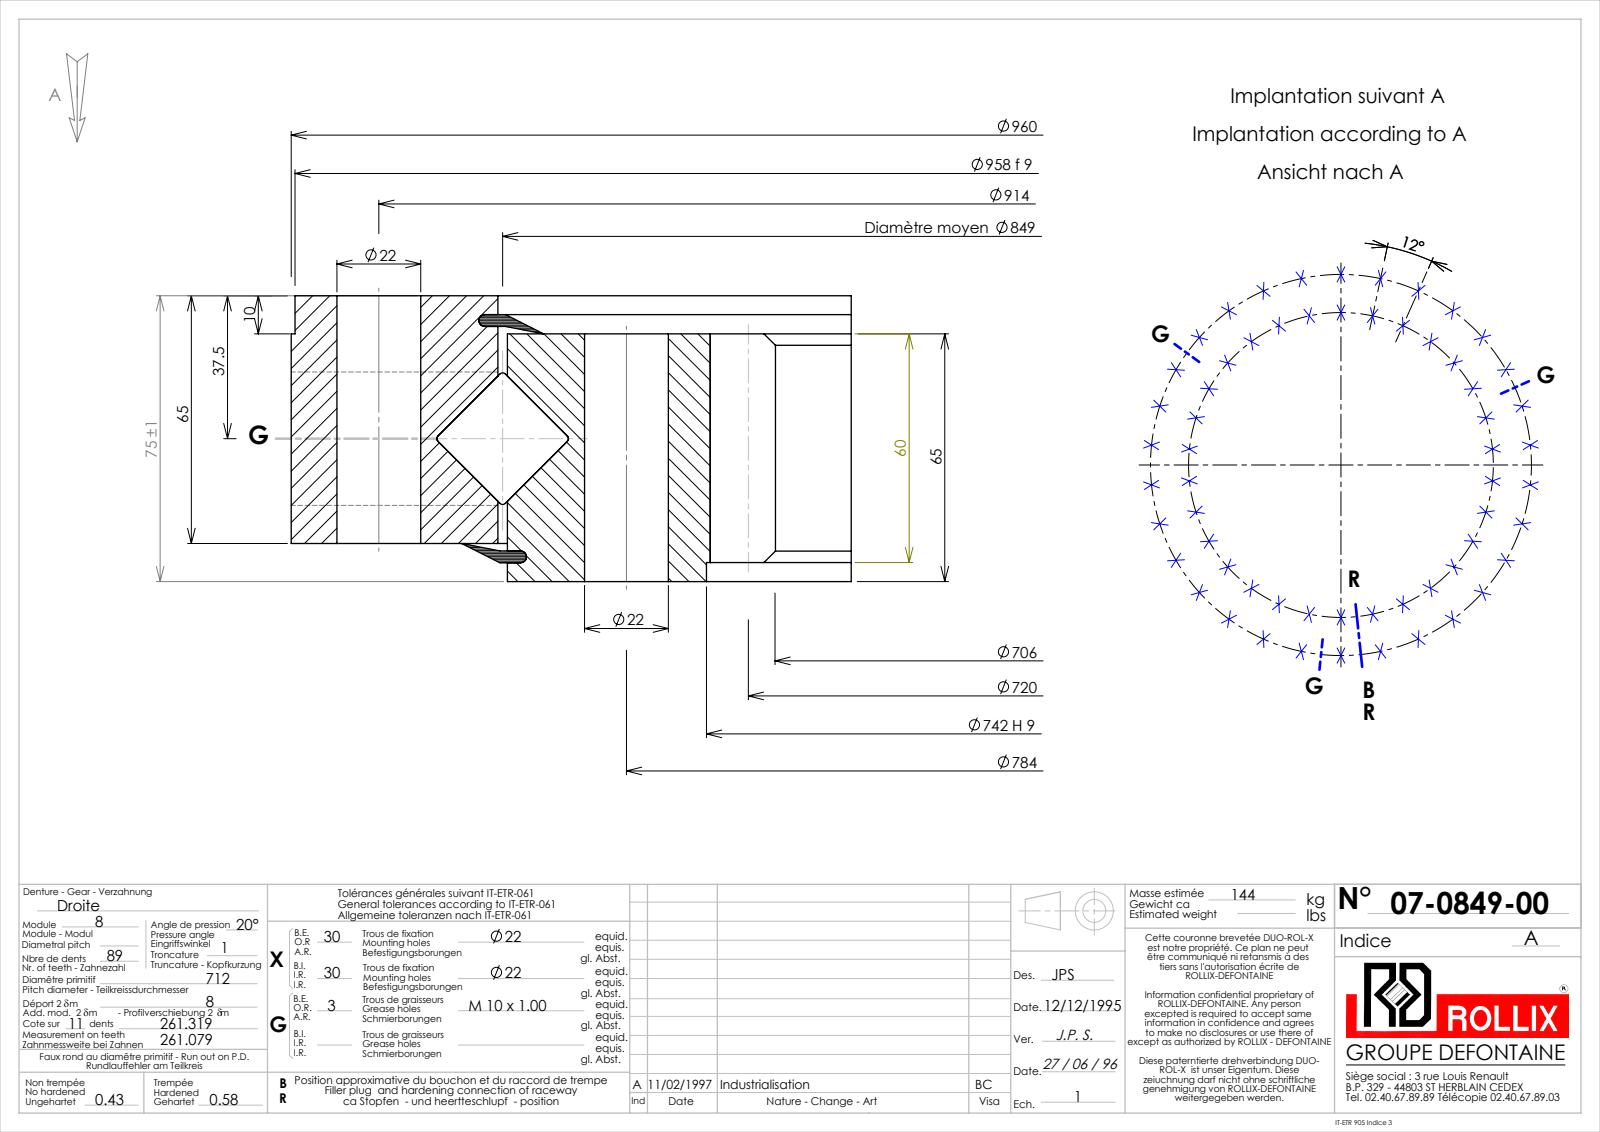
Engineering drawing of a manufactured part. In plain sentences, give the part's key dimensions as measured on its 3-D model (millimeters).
The part is named "07-0849-00". Its 3-D file was written by "SolidWorks 2016 (CONFIG_CONTROL_DESIGN)". It is 5 solids with 738 faces: 194 planar, 325 cylindrical and 219 other. Overall it measures 960 by 960 by 75 millimeters. Its volume is 17 070 000 cubic millimeters and its surface area 1 972 000 square millimeters. Round holes: 60 of diameter 22, 3 of diameter 9, 1 of diameter 742, 1 of diameter 851.5. Round bosses or shafts: 1 of diameter 960, 1 of diameter 958, 1 of diameter 846.5, 1 of diameter 25. Partial cylindrical surfaces (rounded edges, fillets, slot ends): 1 of radius 353, 1 of radius 370. The main face-to-face distances are 10, 65, 55, 75, 4.95, 70.05, 5.05, 60.05, 8.05, 66.95. The hole center spacings are 392, 779.7, 242.27, 163, 678.96, 81.95, 582.62, 766.86.
